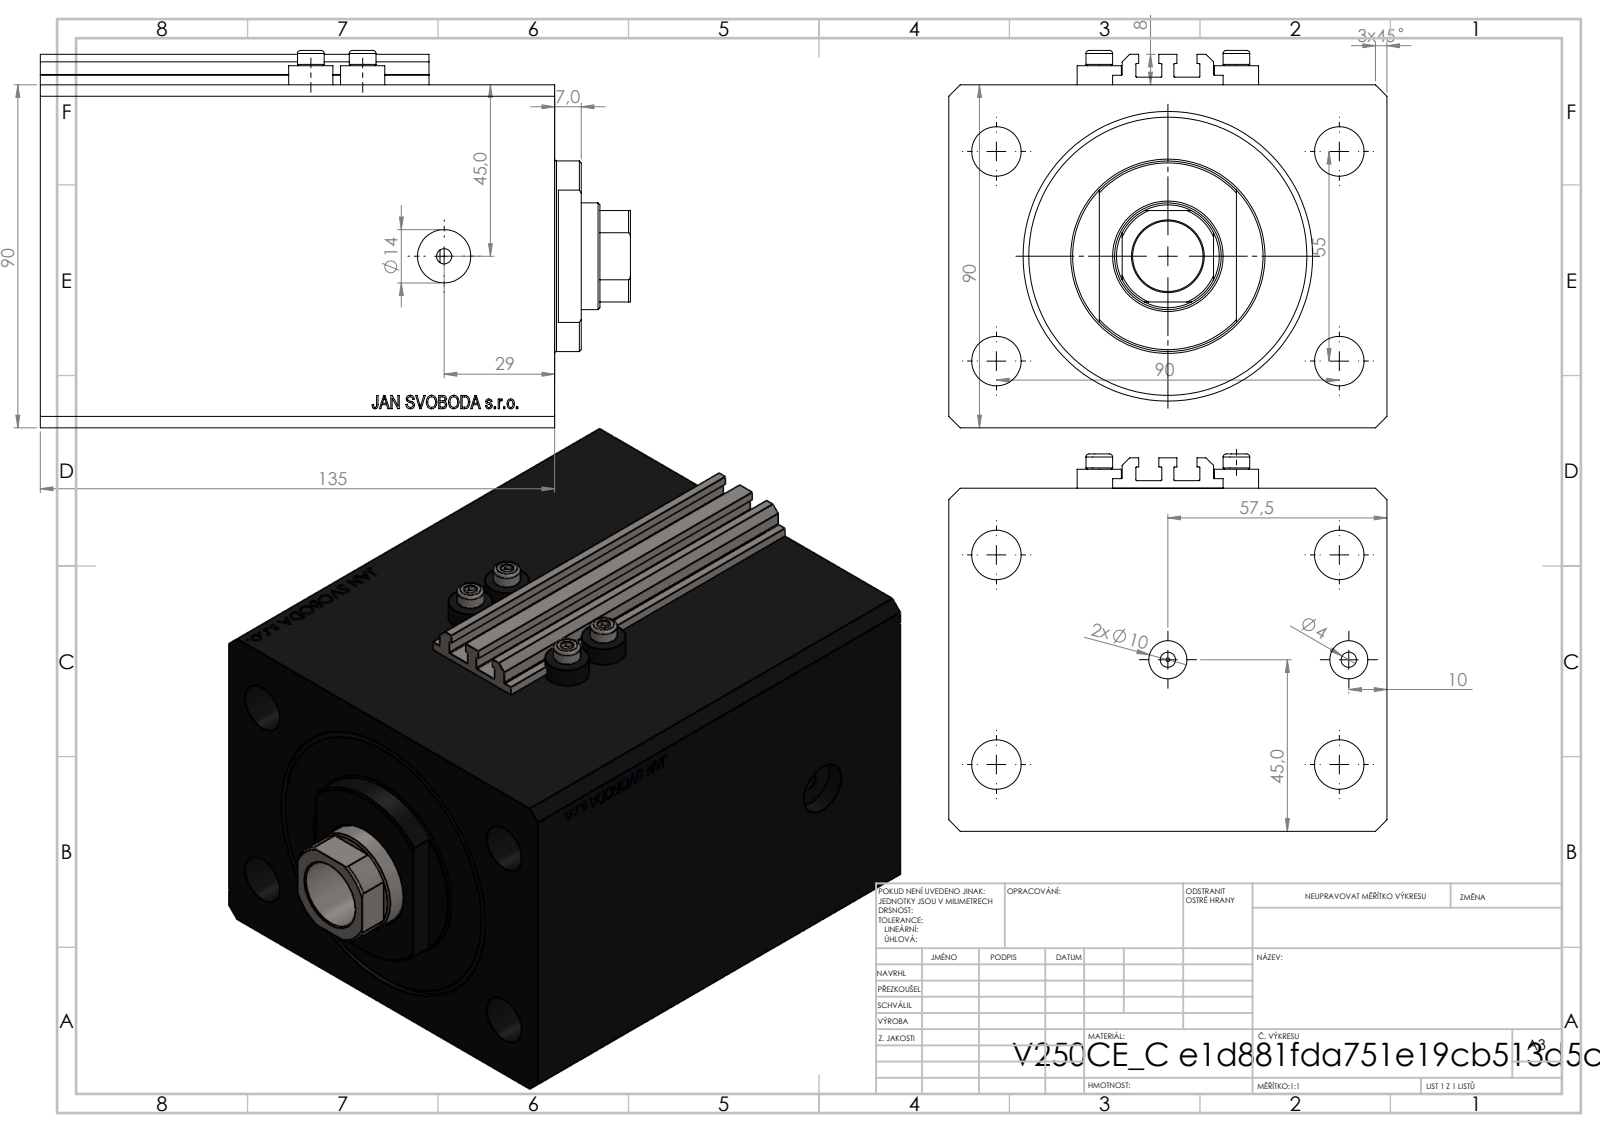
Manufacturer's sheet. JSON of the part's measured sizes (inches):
{"part_name": "V250CE_VC_C; V250CE_C_VCP; ALLEN BOLT V250CE; V250CE_C_Body", "step_written_by": "SolidWorks 2019 (CONFIG_CONTROL_DESIGN)", "units": "inches", "bodies": {"solids": 8, "faces": 1038, "planar": 504, "cylindrical": 88, "other": 446}, "overall_size": [6.098, 4.528, 3.898], "volume_in3": 74.39, "surface_area_in2": 277.9, "round_holes": [[0.157, 8], [0.512, 4], [0.394, 2], [0.551, 2], [0.049, 1], [0.728, 1], [1.102, 1], [2.48, 1], [2.992, 1]], "round_bosses_or_shafts": [[0.457, 4], [0.276, 4], [1.969, 1]], "partial_cylinders_radius": [[0.008, 10], [0.531, 1]], "face_to_face_distances": [3.543, 4.528, 5.315, 0.705, 4.61, 3.425, 4.13, 1.185, 1.969, 2.161], "hole_center_spacings": [2.076, 0.535, 1.087, 1.417, 1.515, 2.165, 3.543, 3.799]}
